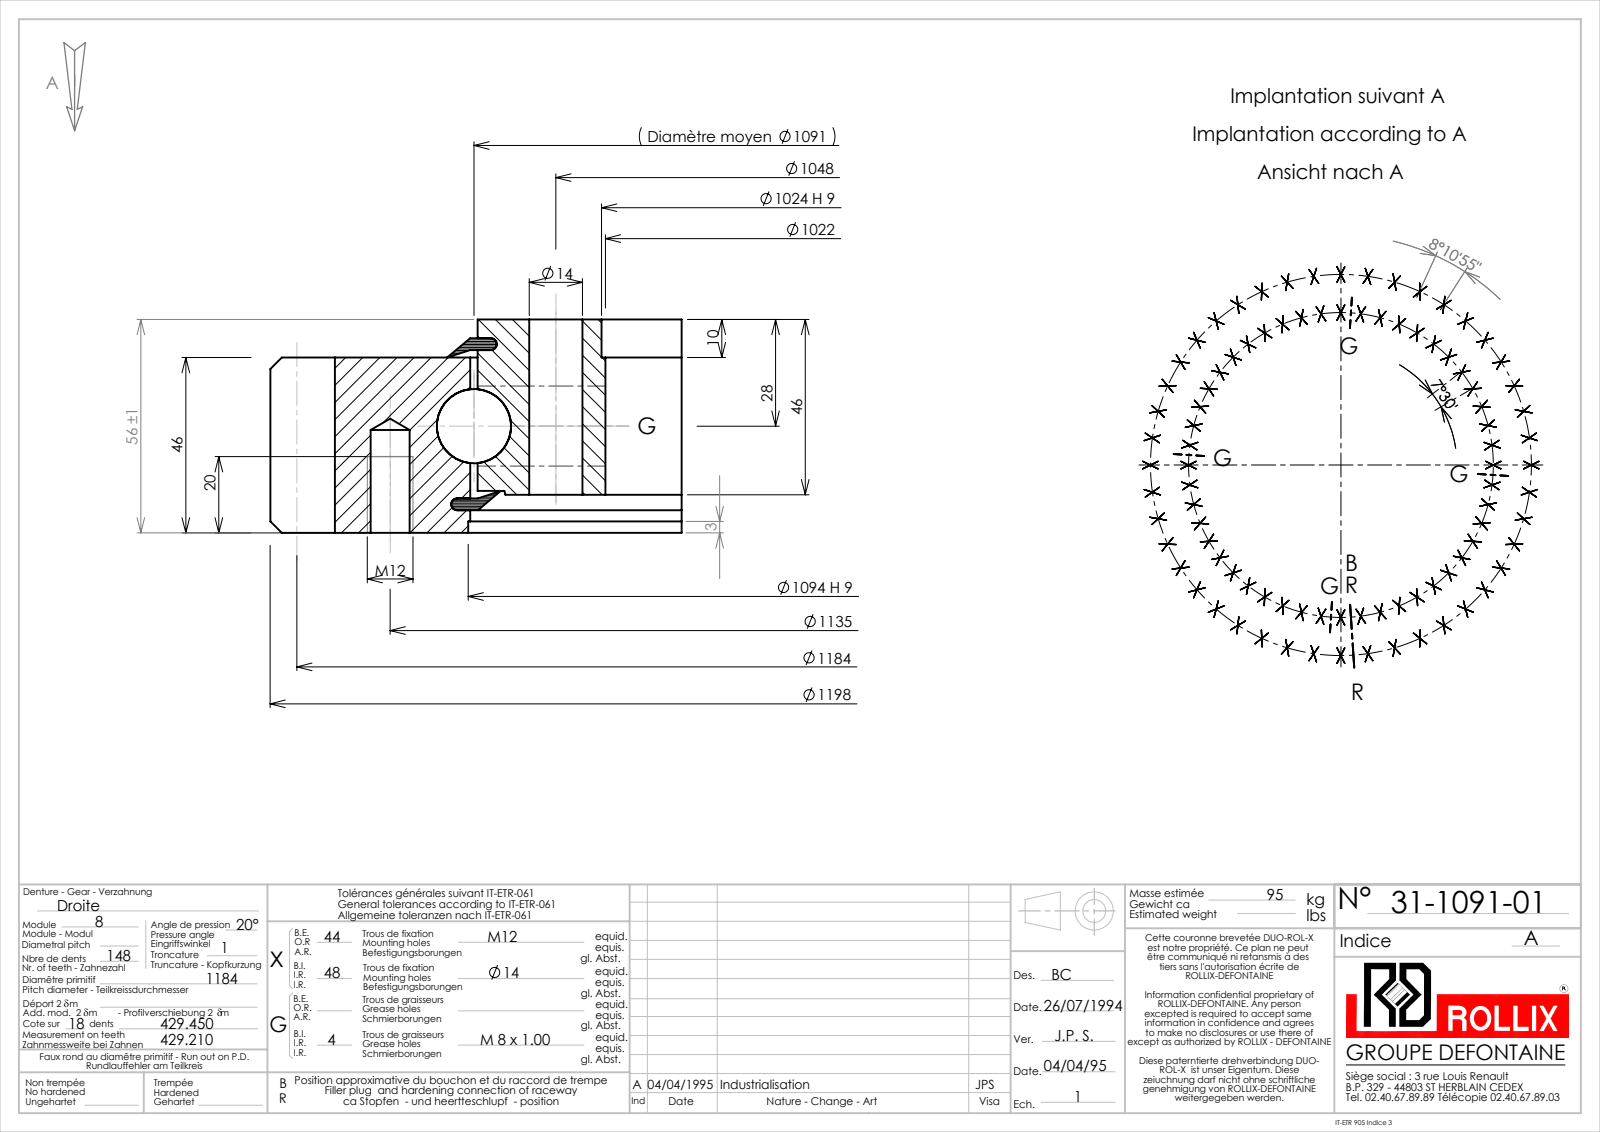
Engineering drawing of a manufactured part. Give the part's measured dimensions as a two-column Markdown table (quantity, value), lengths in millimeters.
| quantity | value |
| --- | --- |
| part name | 31-1091-01 |
| STEP written by | SolidWorks 2016 (CONFIG_CONTROL_DESIGN) |
| units | millimeters |
| bodies | 9 solids, 1320 faces (351 planar, 515 cylindrical, 454 other) |
| overall size | 1197.87 × 1197.87 × 56 |
| volume | 11 180 000 mm³ |
| surface area | 1 787 000 mm² |
| round holes (diameter × count) | 14 × 48, 10.25 × 44, 7 × 4, 1022 × 1, 1024 × 1, 1092.95 × 1, 1094 × 1 |
| round bosses / shafts (diameter × count) | 8 × 4, 1089.05 × 1 |
| partial cylindrical surfaces (radius × count) | 582 × 1, 599 × 1 |
| main face-to-face distances | 46, 10, 56, 36, 3.1, 42, 40.05, 36.95, 5.05, 1.95 |
| hole center spacings | 80.97, 543.95, 241.26, 161.53, 396.64, 471.5, 613.63, 319.76 |
